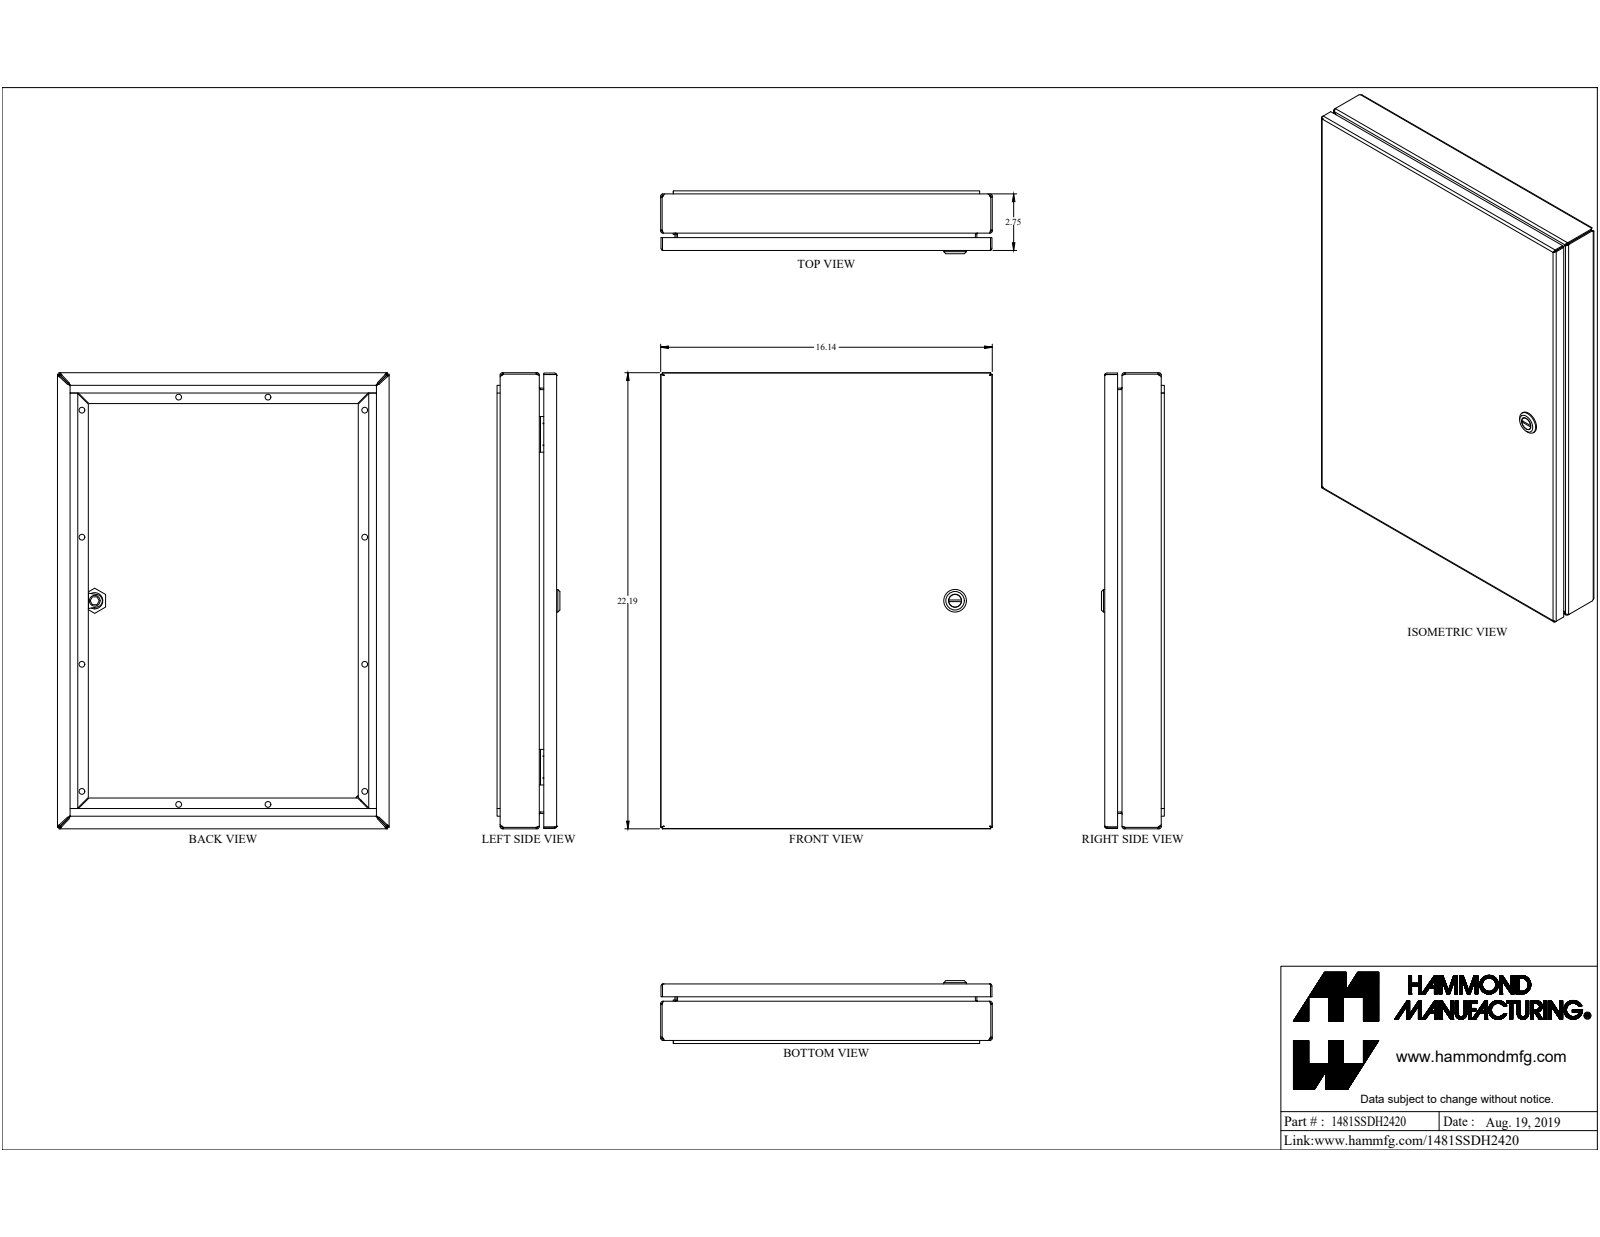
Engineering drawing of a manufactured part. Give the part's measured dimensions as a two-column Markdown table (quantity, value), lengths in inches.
| quantity | value |
| --- | --- |
| part name | 1481SSDH2420 |
| STEP written by | SolidWorks 2019 (CONFIG_CONTROL_DESIGN) |
| units | inches |
| bodies | 24 solids, 622 faces (374 planar, 151 cylindrical, 97 other) |
| overall size | 22.19 × 16.14 × 3.06 |
| volume | 67.99 in³ |
| surface area | 1 779 in² |
| round holes (diameter × count) | 0.281 × 12, 0.172 × 1, 0.197 × 1, 0.24 × 1, 0.242 × 1, 0.387 × 1, 0.5 × 1, 0.63 × 1, 0.768 × 1 |
| round bosses / shafts (diameter × count) | 1.1 × 1, 0.785 × 1, 0.625 × 1, 0.525 × 1, 0.475 × 1, 0.398 × 1, 0.356 × 1, 0.313 × 1 |
| partial cylindrical surfaces (radius × count) | 0.036 × 28, 0.108 × 28, 0.006 × 4, 0.062 × 4, 0.25 × 4, 0.499 × 4, 0.125 × 2, 0.021 × 1 |
| main face-to-face distances | 0.072, 2.578, 0.842, 1.736, 2.65, 16.068, 2.506, 2.678, 1.836, 0.1 |
| hole center spacings | 4.75, 6.182, 9.078, 11.335, 13.764, 15.088, 15.842, 18.502 |
